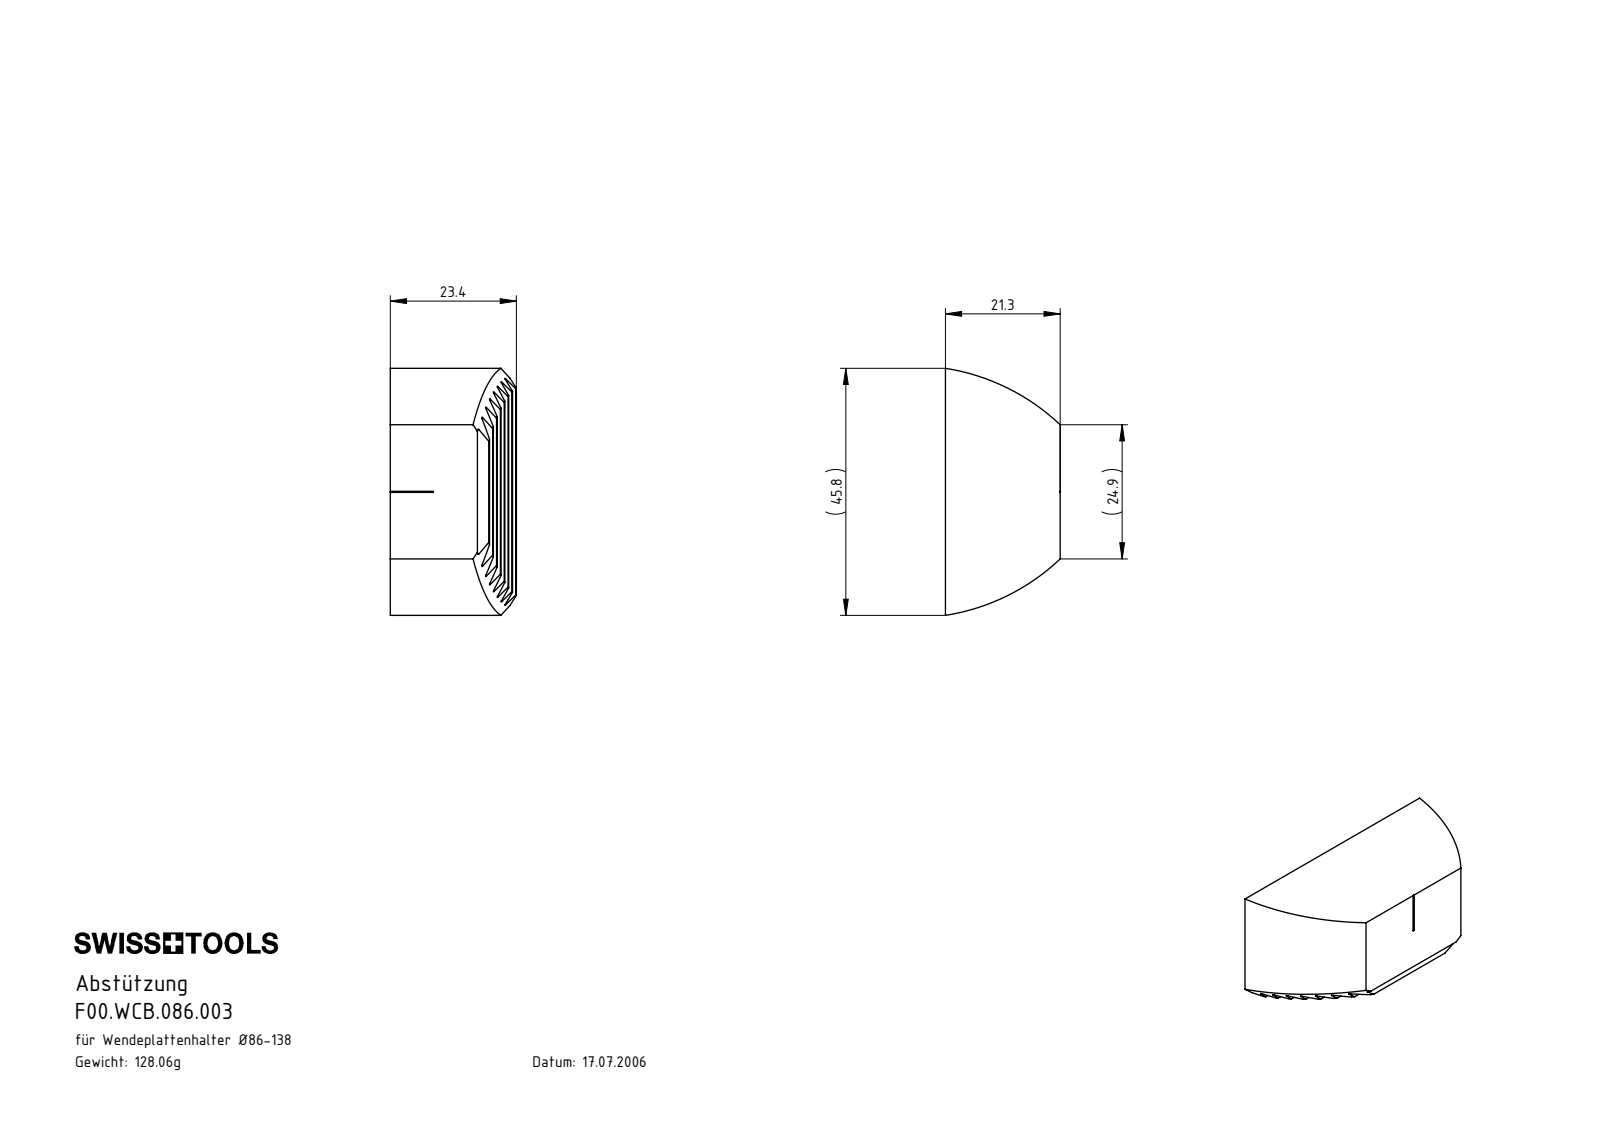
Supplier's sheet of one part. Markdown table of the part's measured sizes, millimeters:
| quantity | value |
| --- | --- |
| part name | F00.WCB.086.003 |
| STEP written by | SolidWorks 2017 (AUTOMOTIVE_DESIGN) |
| units | millimeters |
| bodies | 1 solid, 44 faces (32 planar, 10 cylindrical, 2 other) |
| overall size | 45.83 × 23.4 × 21.3 |
| volume | 16 313 mm³ |
| surface area | 4 497 mm² |
| partial cylindrical surfaces (radius × count) | 0.2 × 8, 40 × 2 |
| main face-to-face distances | 2.38, 4.76, 21.3, 9.53, 7.14, 7.15, 11.91, 4.77, 14.29, 9.52 |
